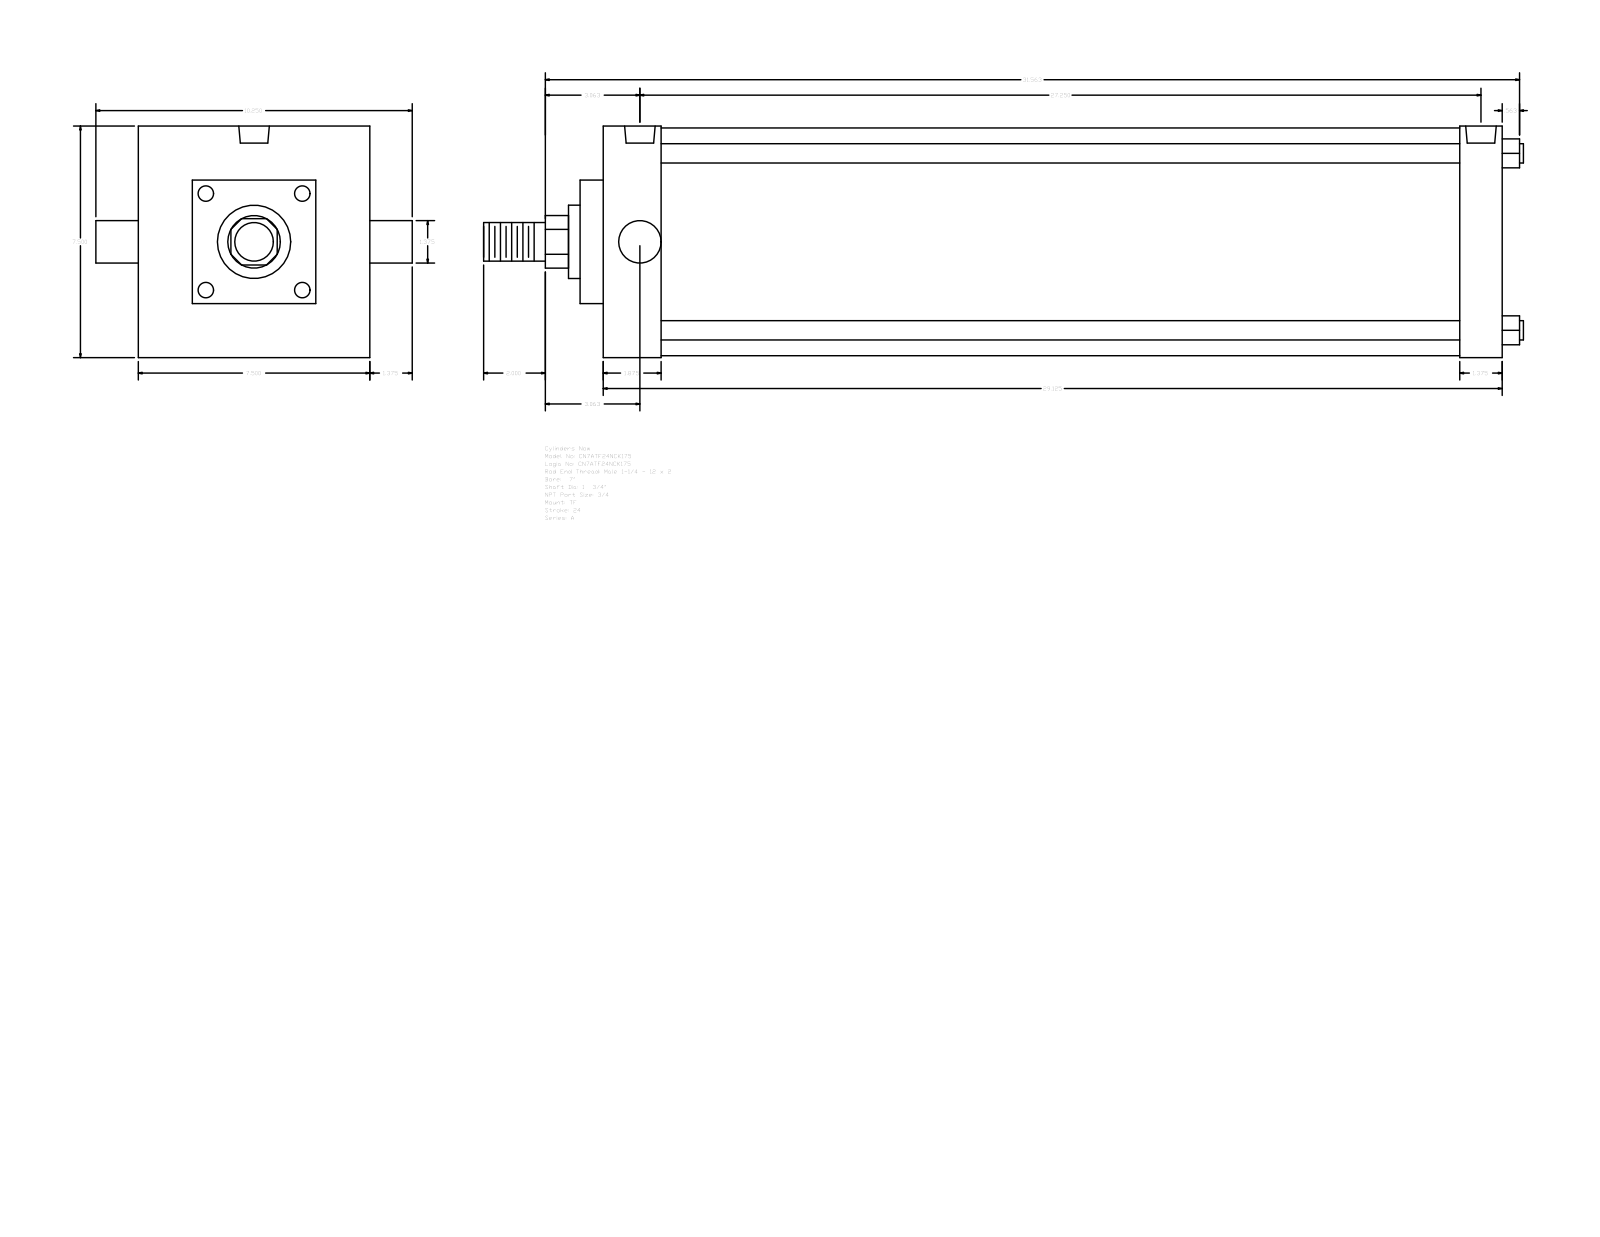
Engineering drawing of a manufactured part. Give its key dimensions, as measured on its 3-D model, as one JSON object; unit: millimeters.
{"part_name": "A_TF__0700_1.75", "step_written_by": "GSSL Pune (CONFIG_CONTROL_DESIGN)", "units": "millimeters", "bodies": {"solids": 0, "faces": 89, "planar": 65, "cylindrical": 24, "other": 0}, "overall_size": [855.66, 260.35, 190.5], "round_holes": [[15.08, 3], [25.12, 2]], "round_bosses_or_shafts": [[15.88, 4], [187.32, 1], [60.33, 1], [44.45, 1], [34.92, 1], [31.75, 1]], "partial_cylinders_radius": [[21.63, 1]], "face_to_face_distances": [190.5, 739.78, 146.05, 19.05, 47.63, 692.15, 704.86, 657.23, 34.92, 44.45], "hole_center_spacings": [5.56, 686.59, 681.03, 692.15]}
